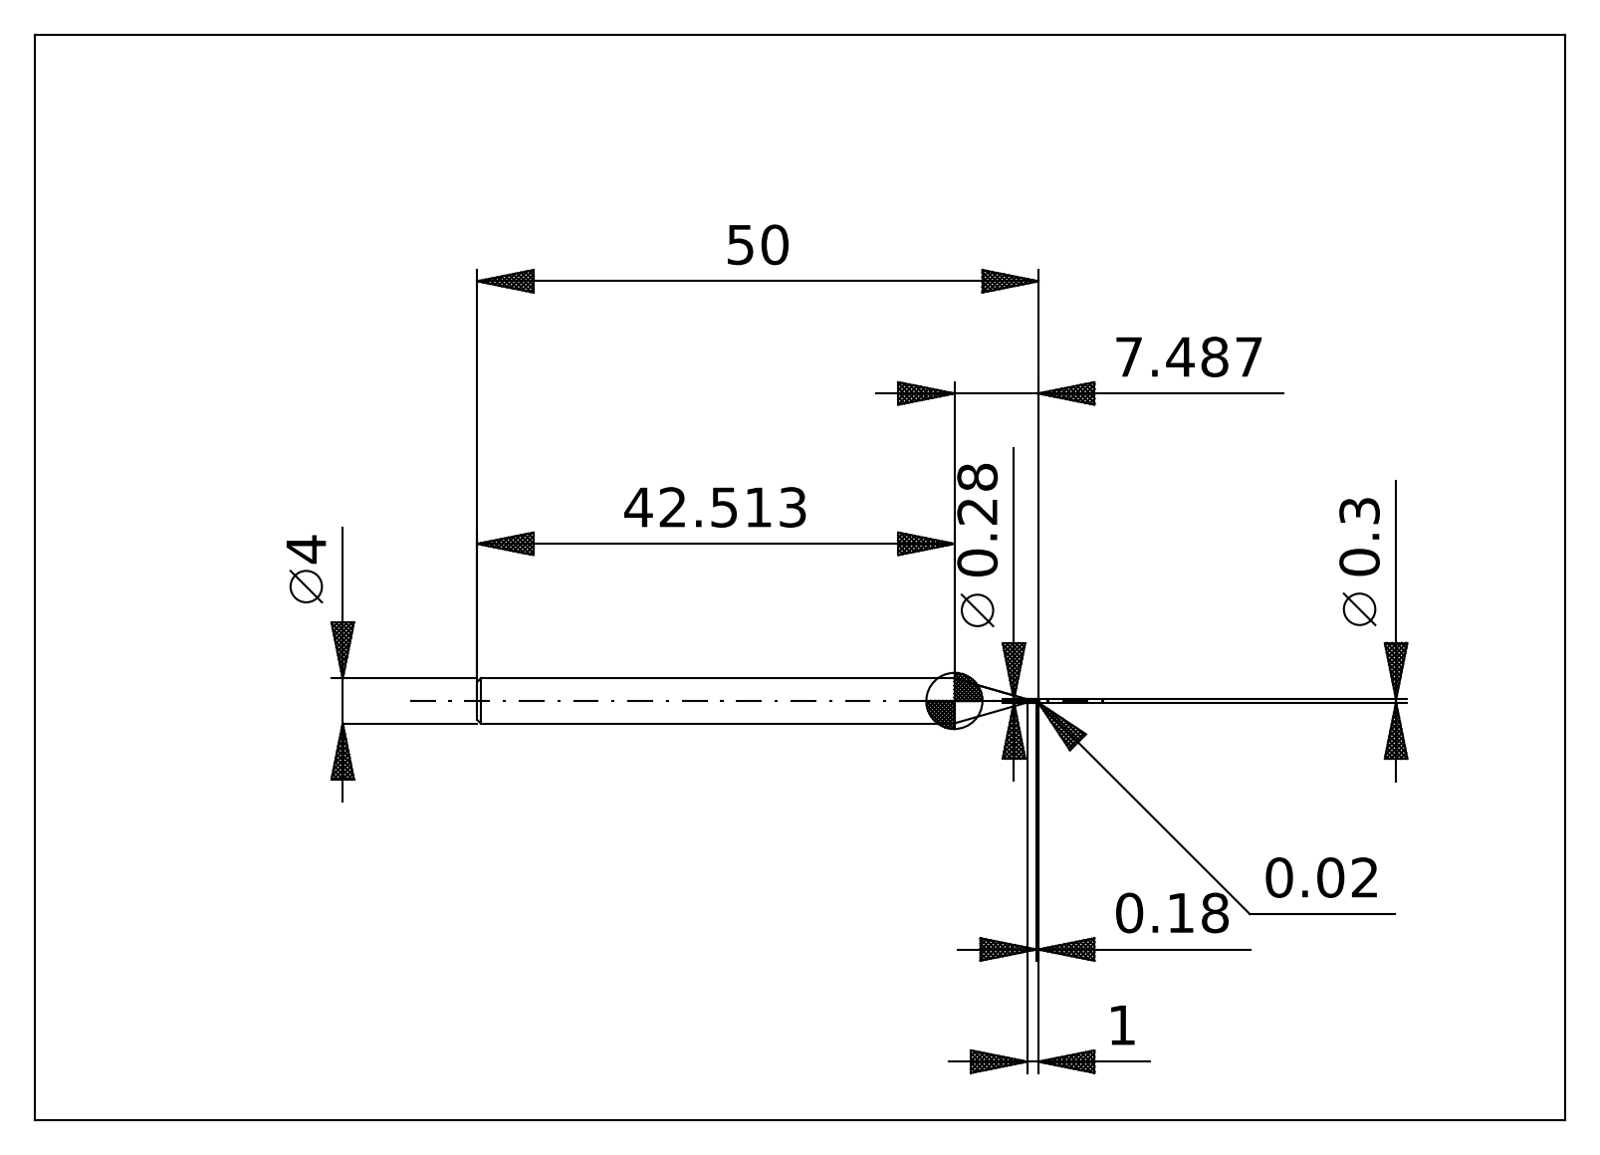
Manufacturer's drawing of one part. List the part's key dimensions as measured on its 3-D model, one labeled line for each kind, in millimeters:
STEP written by: ACIS (automotive_design)
Units: millimetres
Bodies: 2 solids, 26 faces (6 planar, 8 cylindrical, 12 other)
Overall size (bounding box): 50 × 4 × 4
Volume: 563 mm³ · Surface area: 591 mm²
Round bosses / shafts (diameter × count): ⌀4 ×1, ⌀0.28 ×1
Main face-to-face distances: 50, 49.96, 49.82, 7.49, 7.45, 7.31, 42.51
